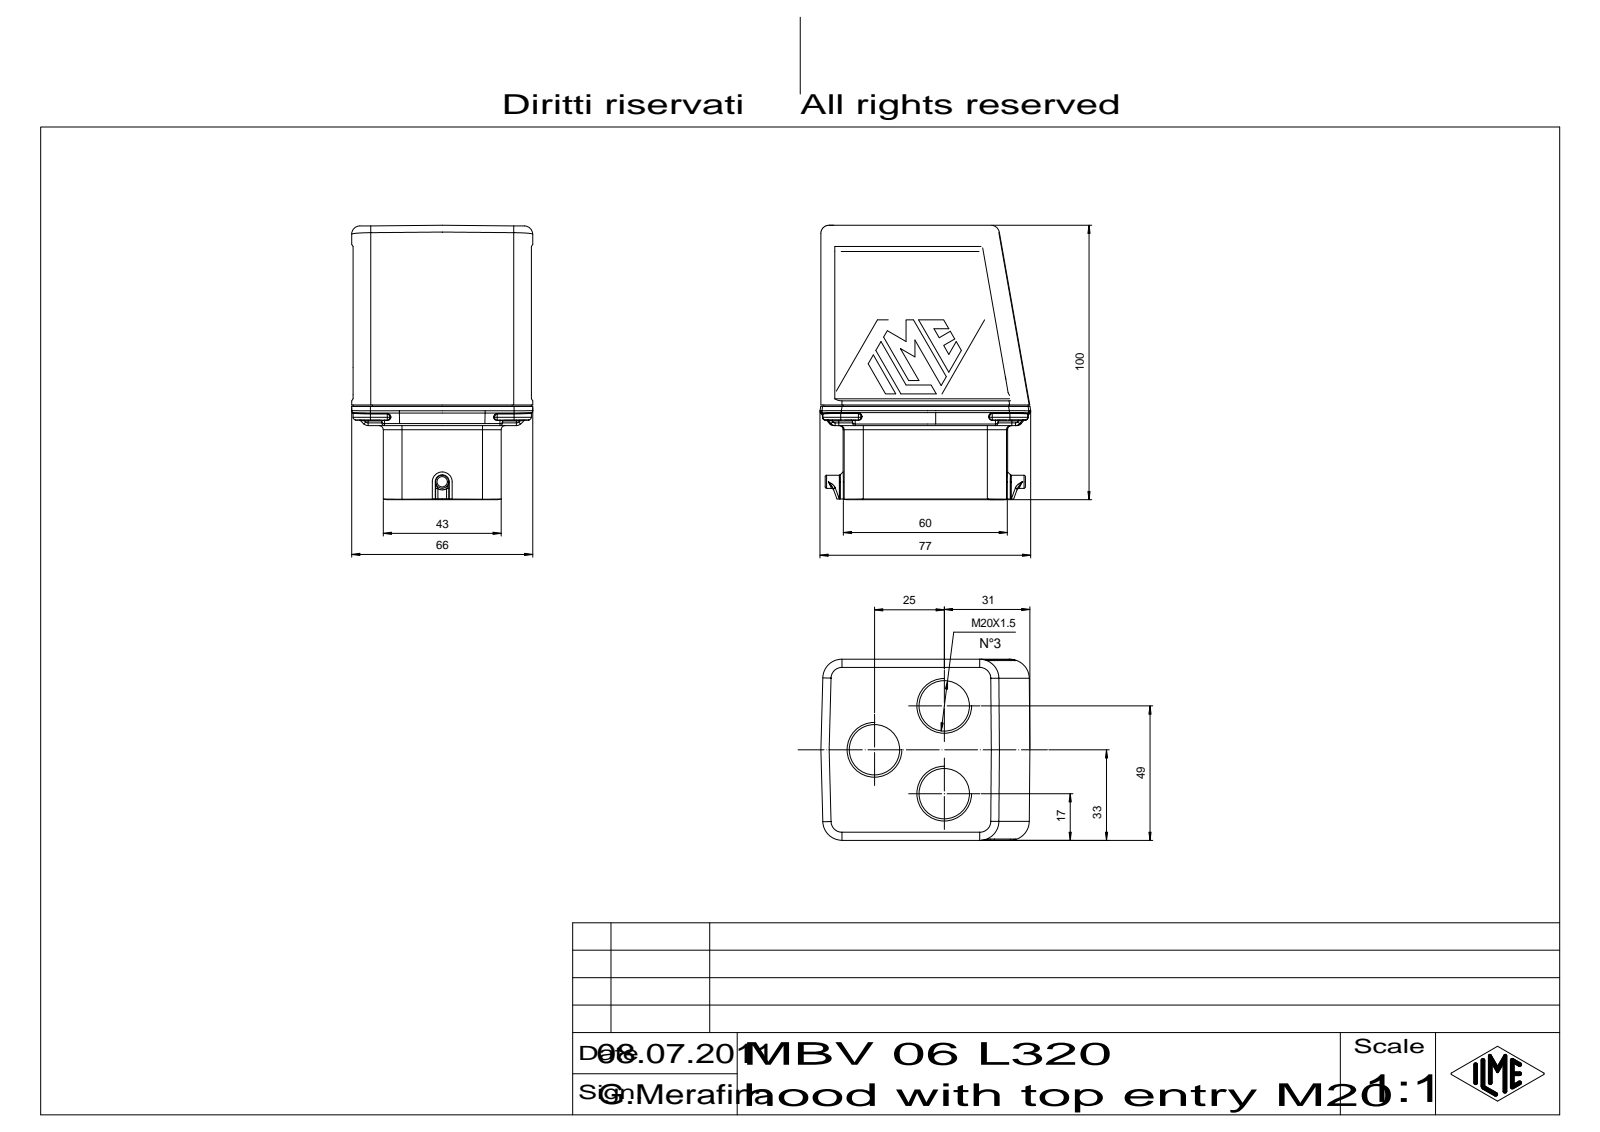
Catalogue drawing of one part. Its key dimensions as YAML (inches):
part_name: "53848_Body_1_Body_1.1"
step_written_by: "CoCreate Modeling 16.00A 16-Aug-2008 (C) Parametric Technology GmbH (AUTOMOTIVE_DESIGN)"
units: inches
bodies: {solids: 1, faces: 567, planar: 267, cylindrical: 144, other: 156}
overall_size: [3.917, 2.983, 2.599]
volume: 19.87
surface_area: 66.54
round_holes:
  - {diameter: 0.724, count: 3}
round_bosses_or_shafts:
  - {diameter: 0.189, count: 1}
partial_cylinders:
  - {radius: 0.039, count: 46}
  - {radius: 0.012, count: 18}
  - {radius: 0.276, count: 14}
  - {radius: 0.118, count: 10}
  - {radius: 0.059, count: 6}
  - {radius: 0.02, count: 4}
  - {radius: 0.165, count: 4}
  - {radius: 0.197, count: 4}
face_to_face_distances: [2.863, 2.559, 0.016, 2.575, 0.433, 2.126, 2.126, 1.693, 0.433, 0.449]
hole_center_spacings: [1.183, 1.26]
